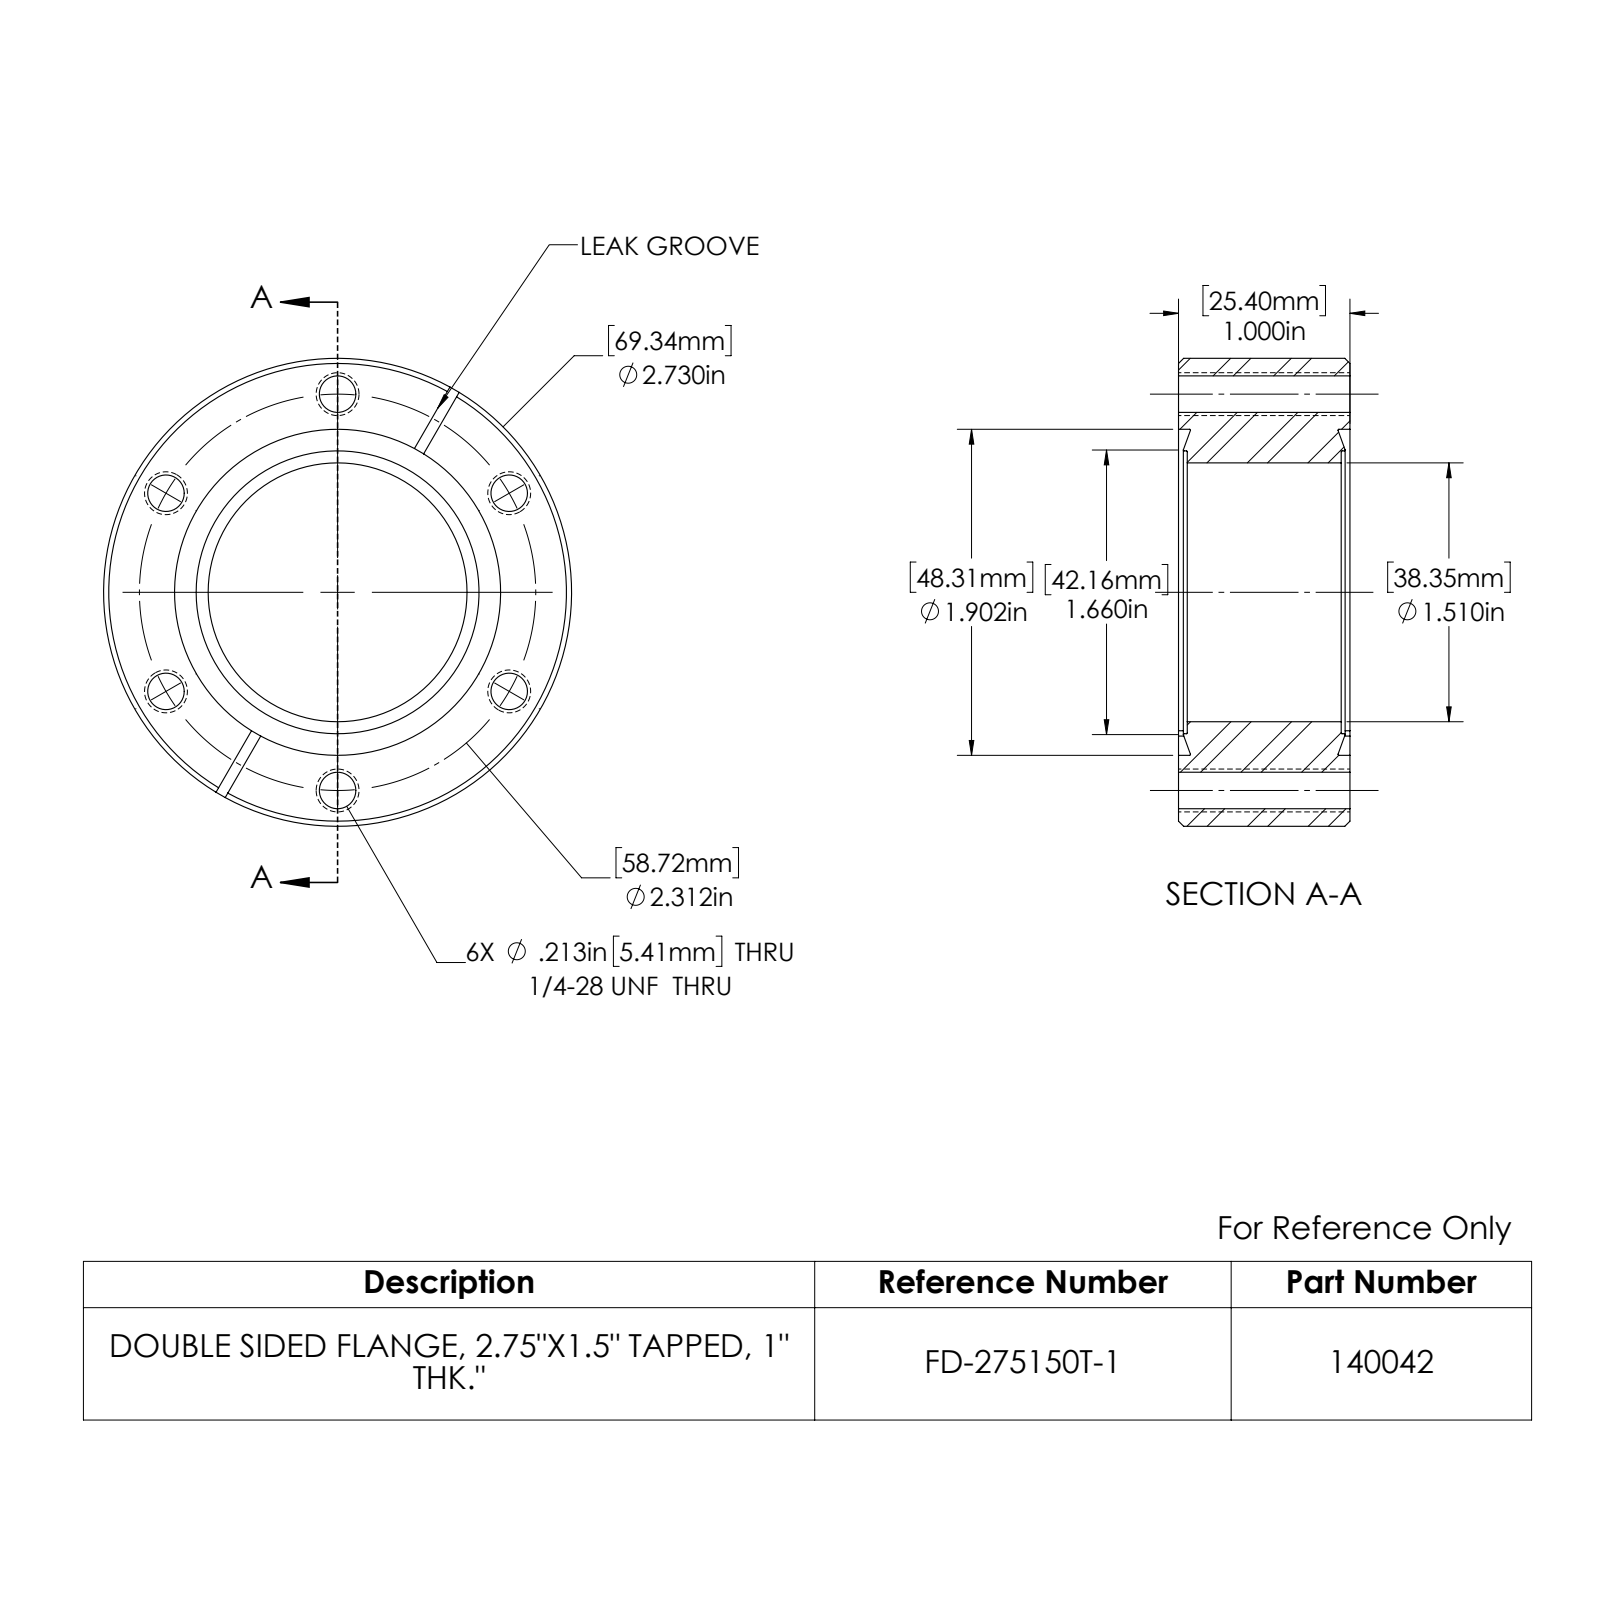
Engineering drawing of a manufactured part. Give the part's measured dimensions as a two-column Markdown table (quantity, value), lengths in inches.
| quantity | value |
| --- | --- |
| part name | 140042_A |
| STEP written by | SolidWorks 2022 (CONFIG_CONTROL_DESIGN) |
| units | inches |
| bodies | 1 solid, 64 faces (14 planar, 28 cylindrical, 22 other) |
| overall size | 2.73 × 2.73 × 1 |
| volume | 3.725 in³ |
| surface area | 25.64 in² |
| round holes (diameter × count) | 0.213 × 6, 1.51 × 1, 1.65 × 1, 1.902 × 1 |
| round bosses / shafts (diameter × count) | 2.73 × 1 |
| partial cylindrical surfaces (radius × count) | 1.25 × 4 |
| main face-to-face distances | 1, 0.051, 0.949, 0.898, 0.062 |
| hole center spacings | 1.156, 2.002, 2.002, 2.312, 2.312 |
